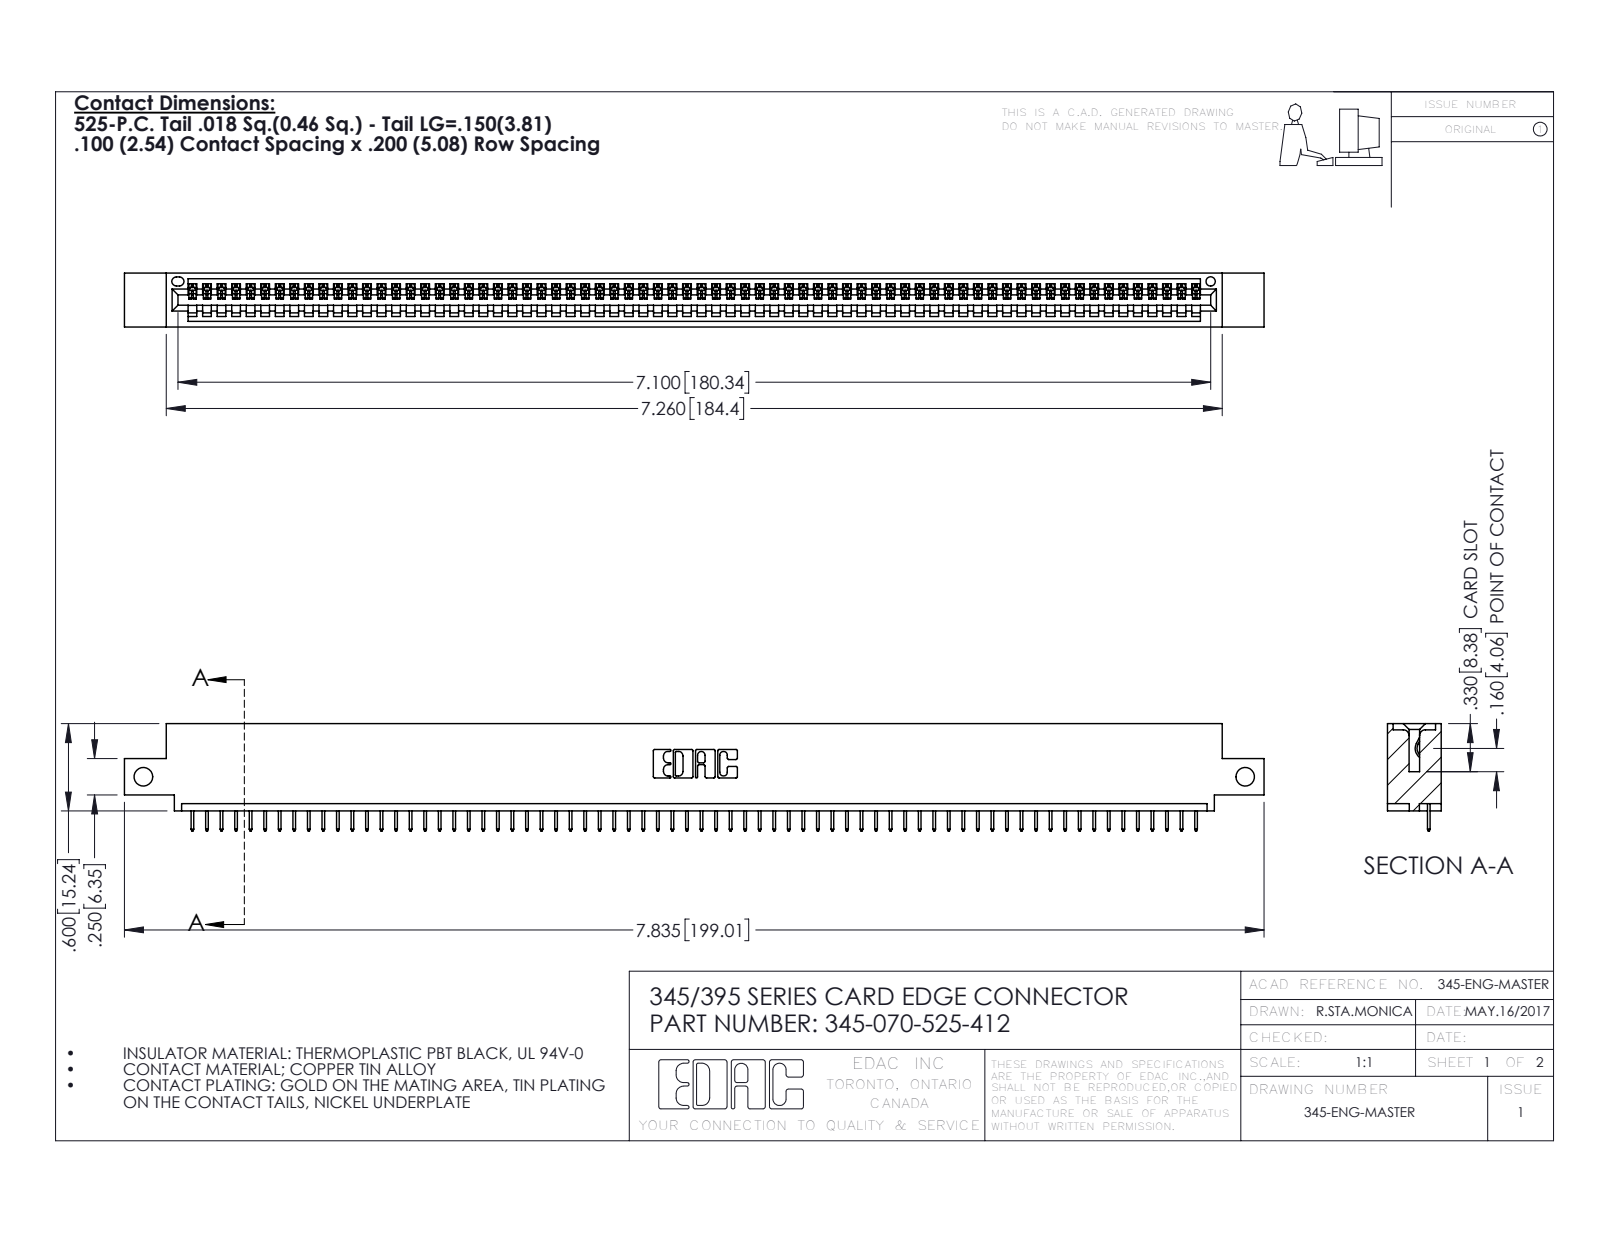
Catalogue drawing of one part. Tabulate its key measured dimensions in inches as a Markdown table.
| quantity | value |
| --- | --- |
| part name | 345-292-001_345-293-125; 345-070-525-412; 345 Part_0.110 Offset - Side Mount |
| STEP written by | SolidWorks 2020 (CONFIG_CONTROL_DESIGN) |
| units | inches |
| bodies | 71 solids, 4470 faces (3304 planar, 1166 cylindrical, 0 other) |
| overall size | 7.835 × 0.737 × 0.37 |
| volume | 1.14 in³ |
| surface area | 37.51 in² |
| round holes (diameter × count) | 0.128 × 2, 0.064 × 1 |
| partial cylindrical surfaces (radius × count) | 0.006 × 140, 0.01 × 22, 0.007 × 6, 0.031 × 6, 0.026 × 3, 0.031 × 2, 0.04 × 2, 0.014 × 1 |
| main face-to-face distances | 0.072, 0.298, 0.37, 0.2, 0.098, 0.272, 0.025, 0.225, 0.072, 0.149 |
| hole center spacings | 7.575 |
